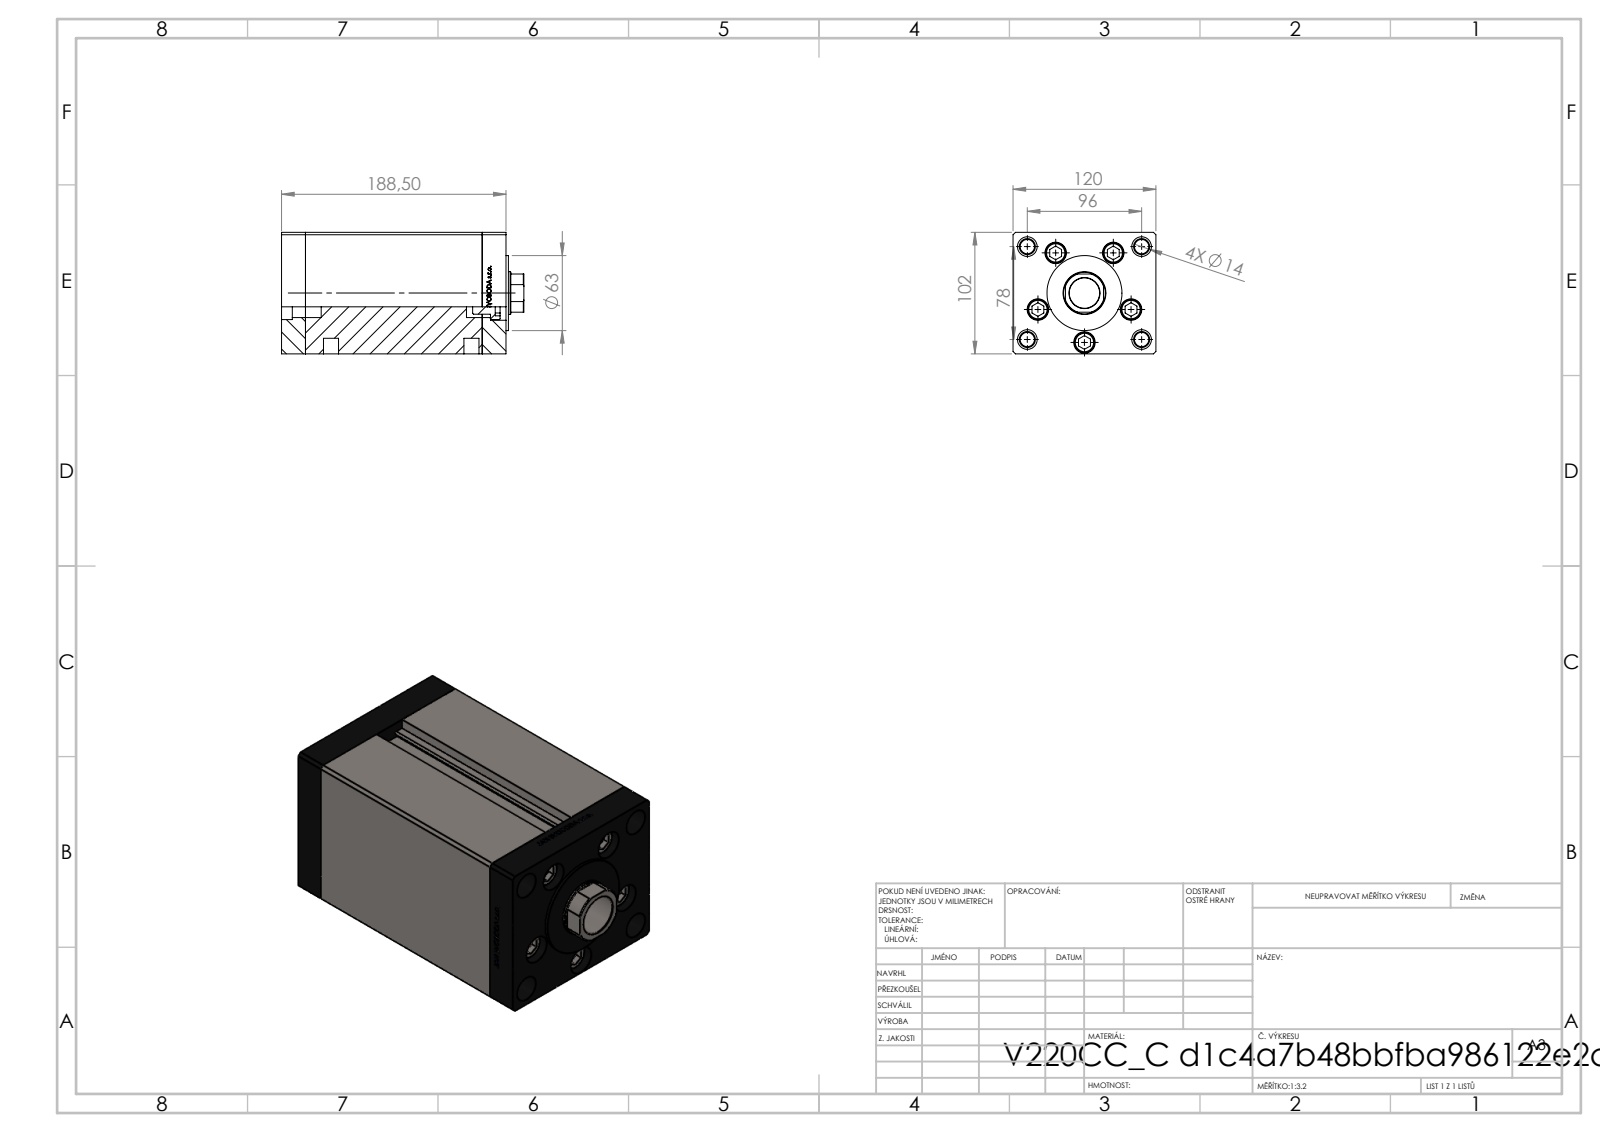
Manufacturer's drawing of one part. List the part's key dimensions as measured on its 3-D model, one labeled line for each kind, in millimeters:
Part name (STEP PRODUCT): V220C FRONT; V220C_C MIDDLE; ALLEN BOLT; V220C_VC_C (+1 more)
STEP written by: SolidWorks 2019 (CONFIG_CONTROL_DESIGN)
Units: millimetres
Bodies: 13 solids, 1185 faces (546 planar, 177 cylindrical, 462 other)
Overall size (bounding box): 203.5 × 120 × 102
Volume: 1 944 000 mm³ · Surface area: 281 515 mm²
Round holes (diameter × count): ⌀13.5 ×9, ⌀18 ×5, ⌀2 ×4, ⌀12 ×4, ⌀13.16 ×4, ⌀16.5 ×4, ⌀17 ×1, ⌀25.5 ×1, ⌀36 ×1
Round bosses / shafts (diameter × count): ⌀8 ×5, ⌀17 ×4, ⌀63 ×1
Partial cylindrical surfaces — rounded edges, fillets, slot ends (radius × count): R0.93 ×2, R17.5 ×1
Main face-to-face distances: 120, 20, 102, 148.5, 168.5, 34.25, 188.5, 154.25, 134.25, 14.25
Hole centre spacings: 41.5, 61.85, 24.39, 26.69, 47.92, 48.07, 49.84, 53.57
